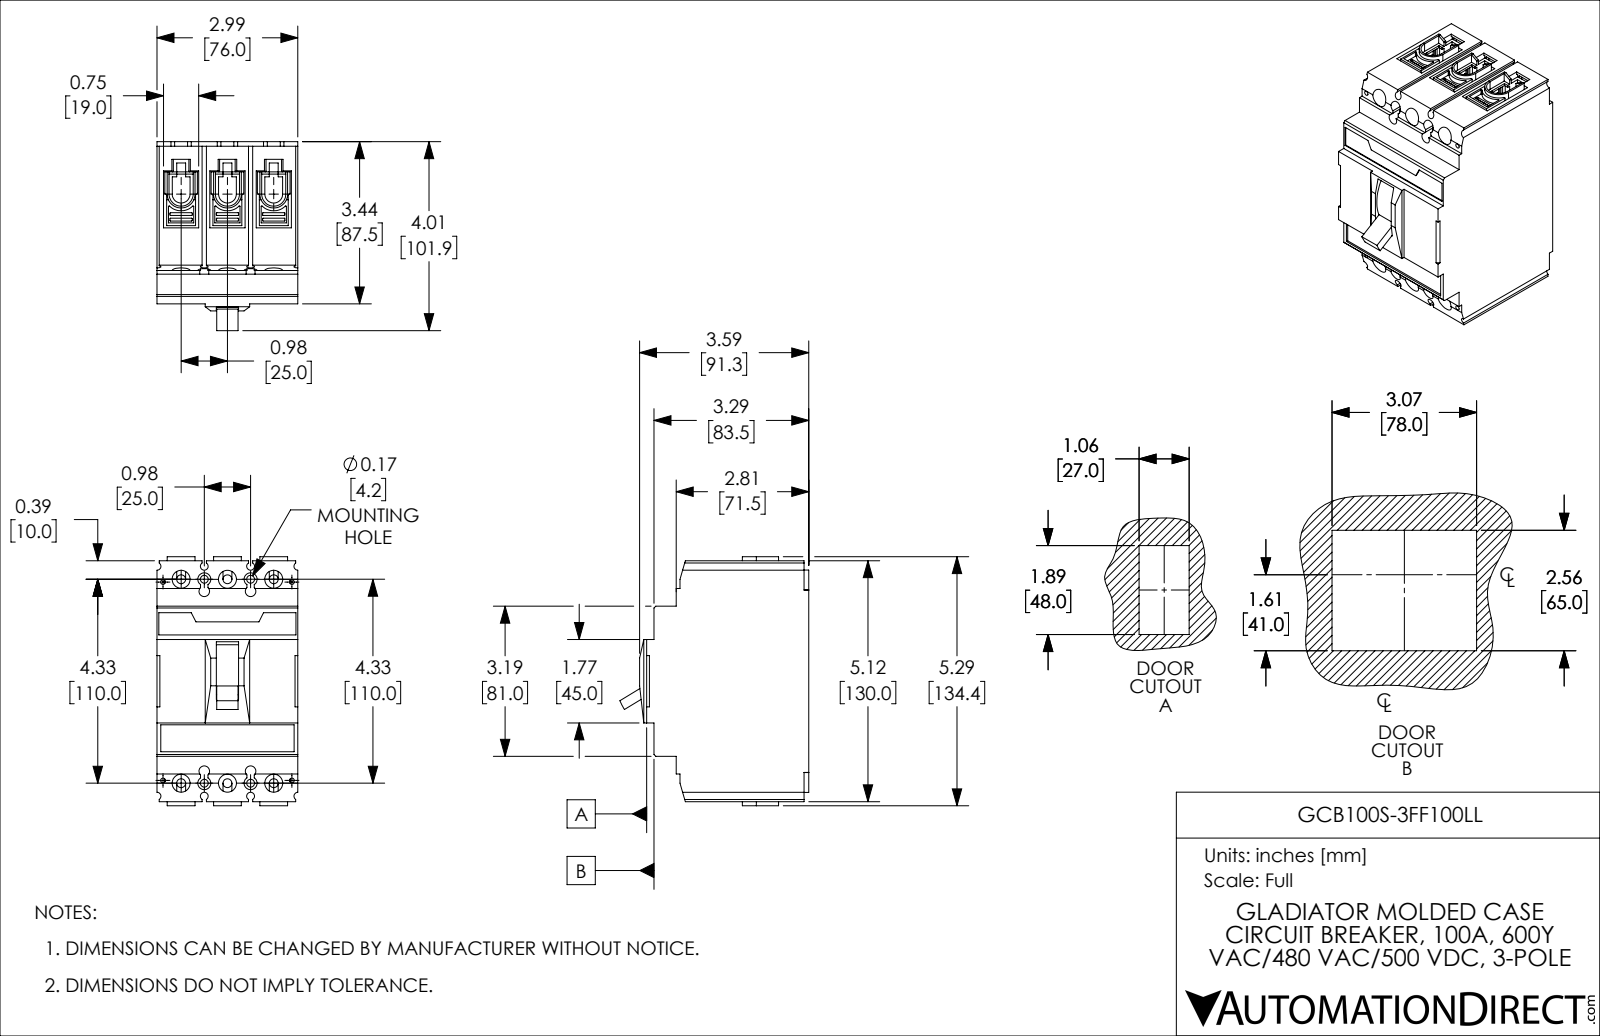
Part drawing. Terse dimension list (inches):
name: GCB100S-3FF100LL
written by: SolidWorks 2021 (CONFIG_CONTROL_DESIGN)
unit: in
bodies: 1 solid, 1256 faces (784 planar, 424 cylindrical, 48 other)
size: 5.291 × 4.013 × 2.992
volume: 43.23 in³; area: 148.5 in²
holes: 8× ⌀0.165, 6× ⌀0.189, 6× ⌀0.382, 4× ⌀0.098, 4× ⌀0.276
rounds: 86× R0.012, 38× R0.02, 14× R0.039, 14× R0.157, 6× R0.024, 4× R0.083, 4× R0.112, 3× R0.189
face distances: 2.992, 0.984, 0.622, 4.496, 1.732, 0.11, 3.445, 0.748, 1.969, 5.118
hole spacings: 0.492, 0.564, 0.984, 4.359, 4.633, 4.441, 4.331, 0.276
